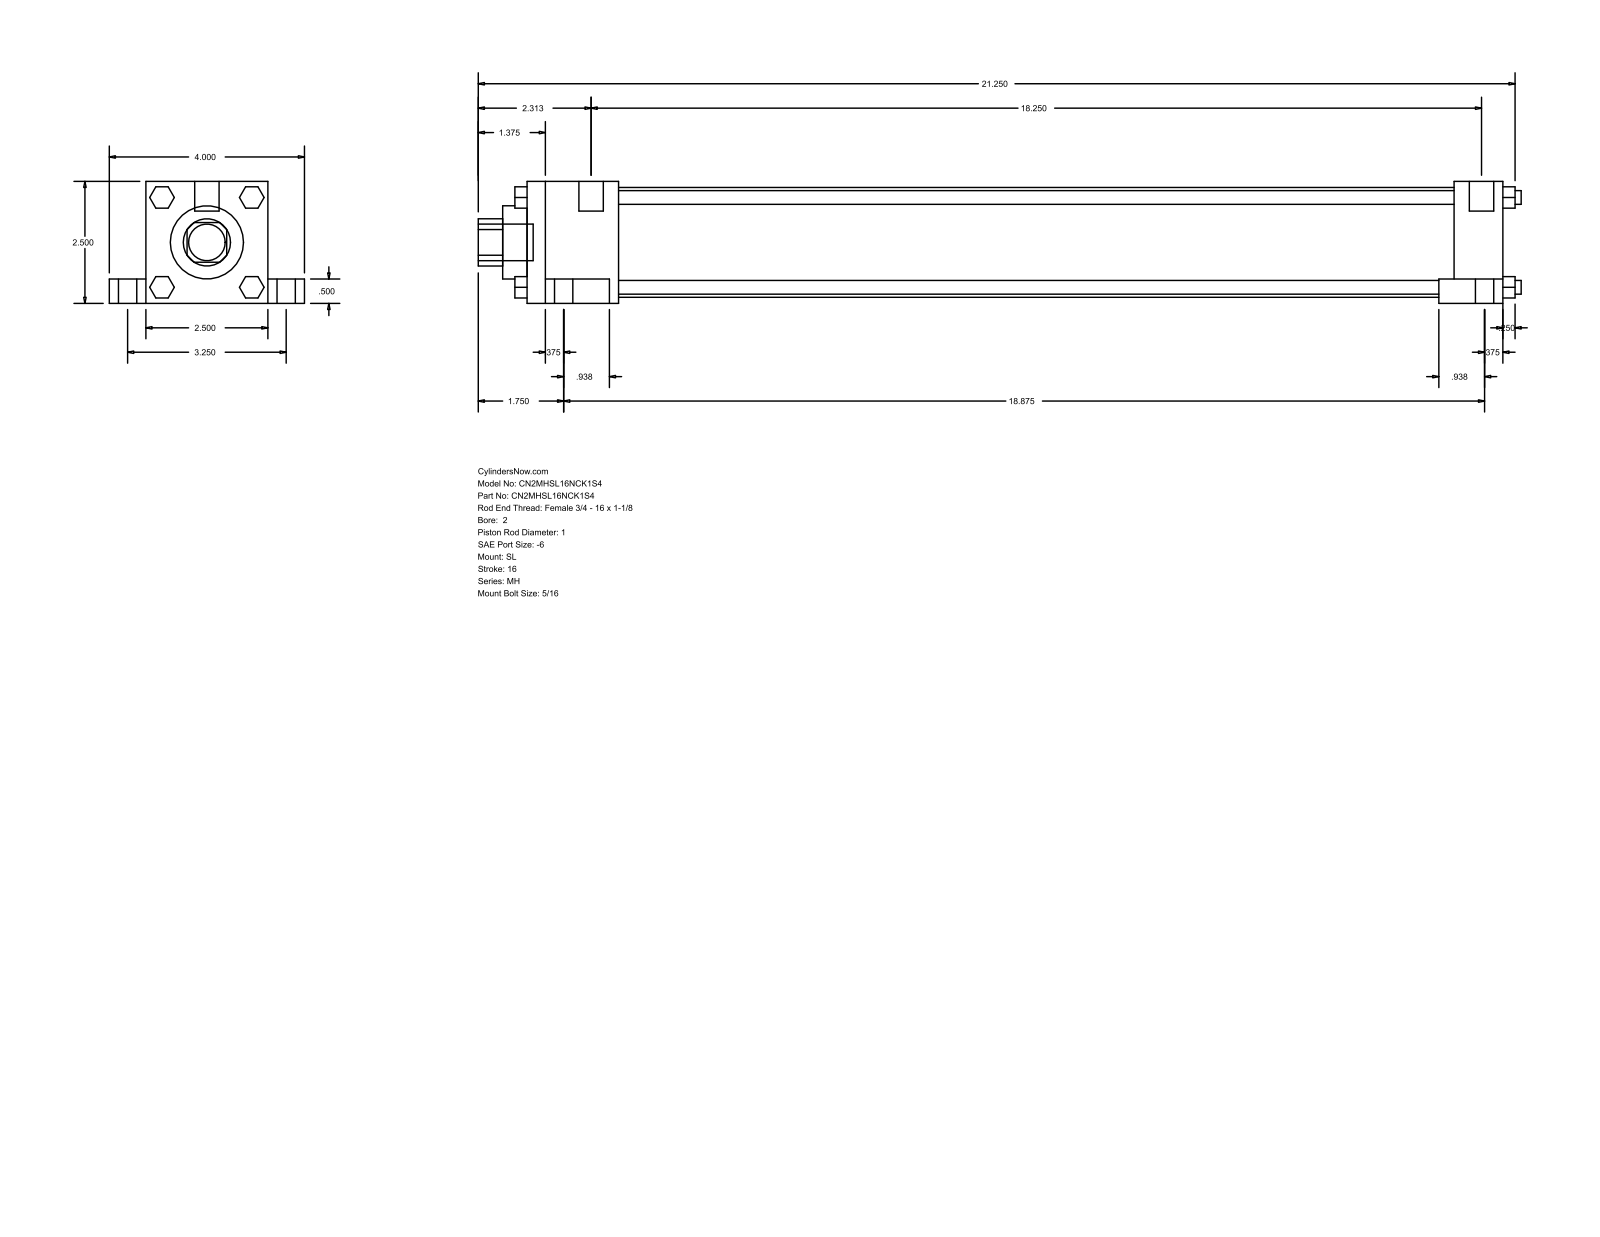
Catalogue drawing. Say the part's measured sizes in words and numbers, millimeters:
The part is named "MH_SL__0200_1". Its 3-D file was written by "GSSL Pune (CONFIG_CONTROL_DESIGN)". It is 0 solids with 148 faces: 112 planar, 36 cylindrical and 0 other. Overall it measures 542.92 by 101.6 by 63.5 millimeters. Round holes: 1 of diameter 25.4, 1 of diameter 38.1, 1 of diameter 57.15. Round bosses or shafts: 4 of diameter 15.88, 4 of diameter 9.53, 4 of diameter 7.14, 4 of diameter 5.56, 2 of diameter 12.7, 1 of diameter 19.05. Partial cylindrical surfaces (rounded edges, fillets, slot ends): 1 of radius 12.29. The main face-to-face distances are 63.5, 508, 12.7, 19.05, 50.8, 82.55, 9.52, 25.4, 482.6, 47.63.
